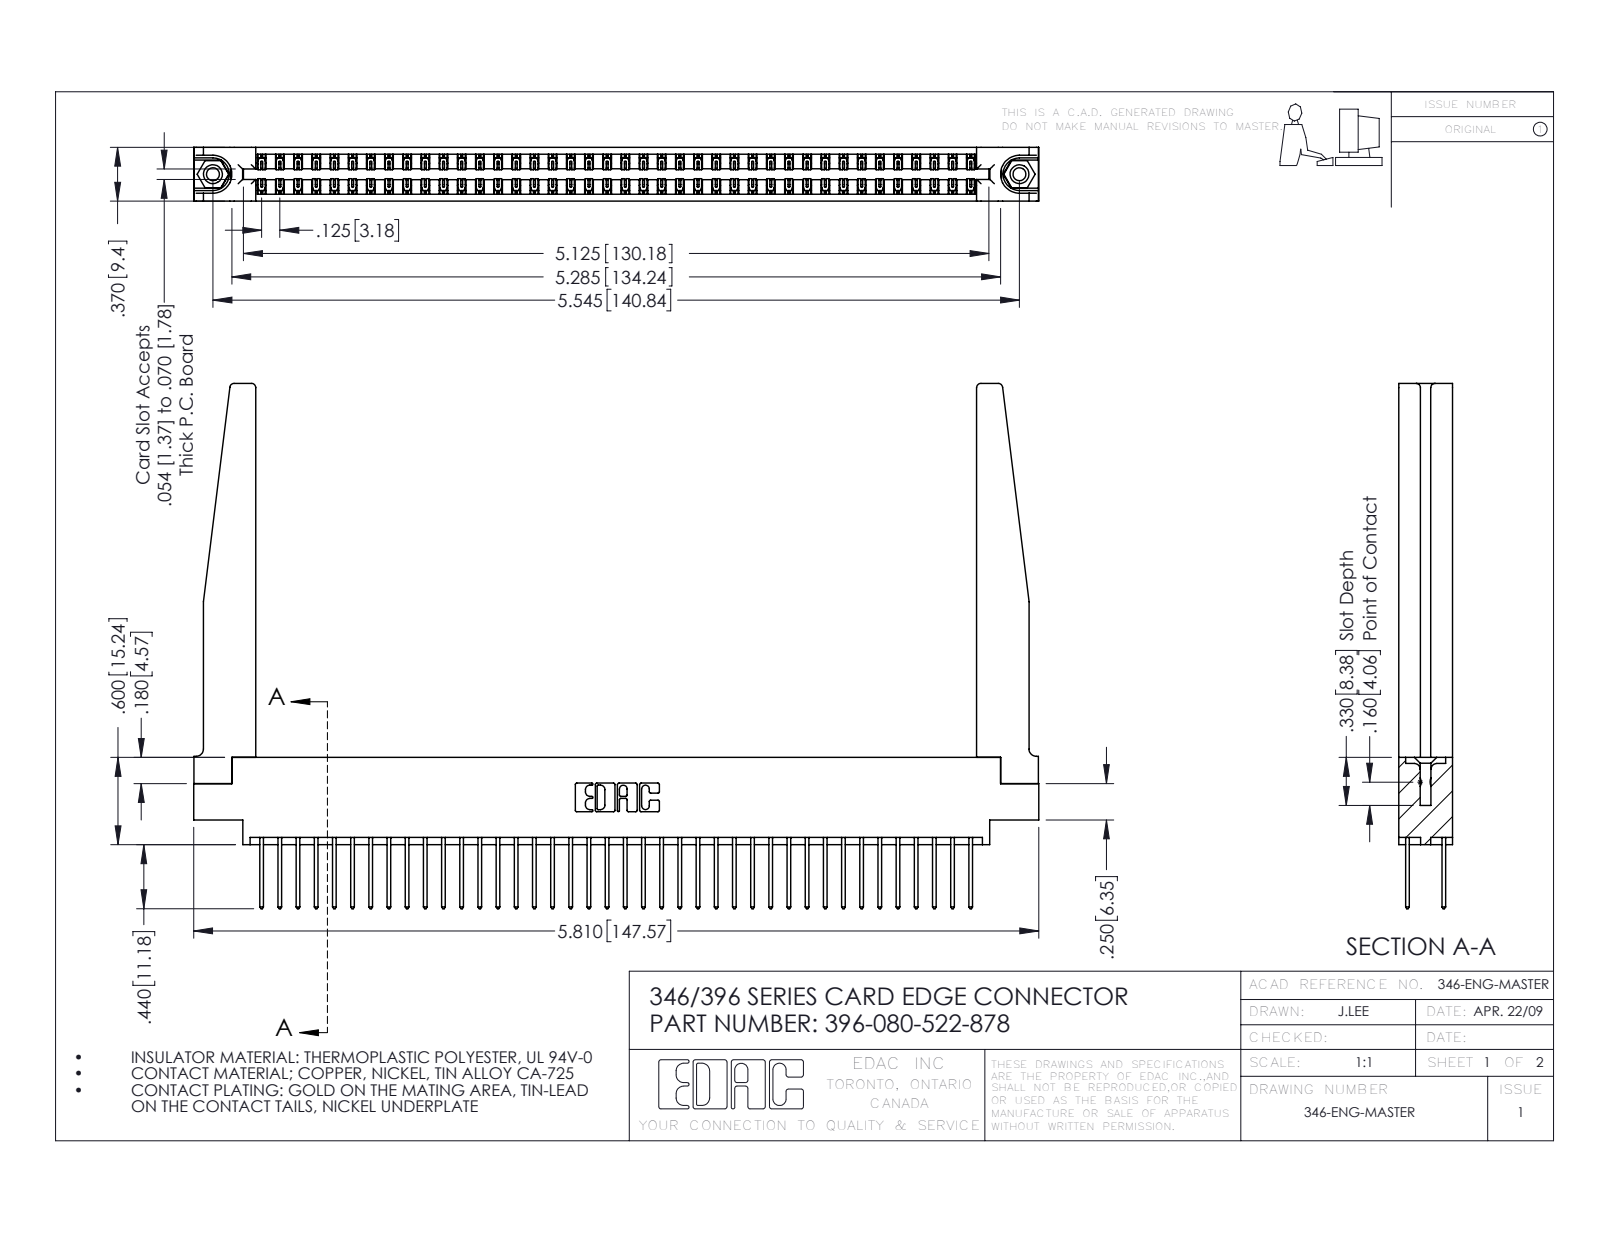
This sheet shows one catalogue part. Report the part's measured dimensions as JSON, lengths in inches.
{"part_name": "345-292-001_345-293-122; 396-080-522-878; 346-220-078_345-220-078; 345-250-001_345-250-001-102 (+1 more)", "step_written_by": "SolidWorks 2016 (CONFIG_CONTROL_DESIGN)", "units": "inches", "bodies": {"solids": 85, "faces": 4520, "planar": 3022, "cylindrical": 1446, "other": 52}, "overall_size": [5.81, 3.61, 0.37], "volume_in3": 1.302, "surface_area_in2": 42.57, "round_holes": [[0.089, 2], [0.125, 2], [0.156, 2], [0.064, 1]], "round_bosses_or_shafts": [[0.155, 2]], "partial_cylinders_radius": [[0.006, 120], [0.01, 80], [0.01, 22], [0.03, 8], [0.007, 6], [0.031, 6], [0.026, 3], [0.014, 2]], "face_to_face_distances": [0.37, 0.048, 0.322, 0.072, 0.25, 0.298, 0.025, 0.148, 0.15, 0.275], "hole_center_spacings": [0.246, 5.336, 5.545]}
